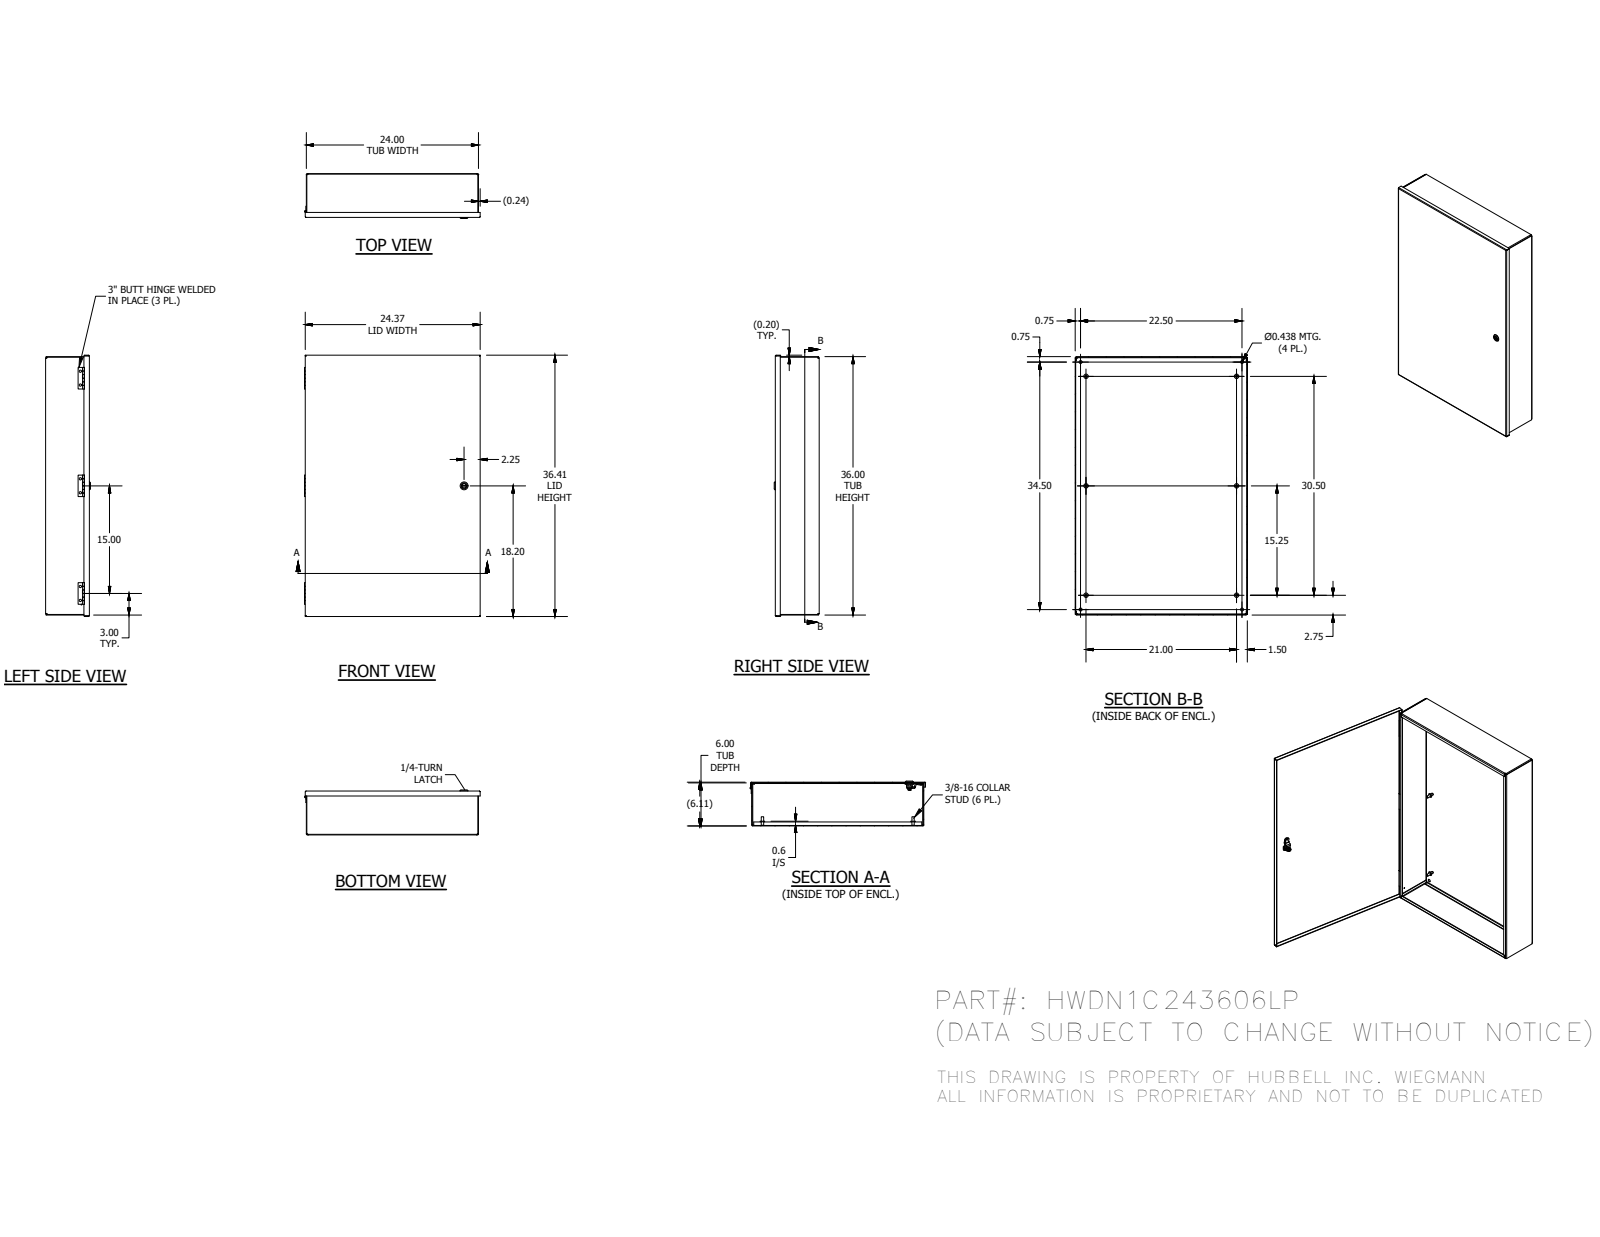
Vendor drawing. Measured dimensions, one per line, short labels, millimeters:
name: N1C243606LPBLR; N1C2406LPTB; N1C2436LPLID; 1000-101-GPF_GPD (+8 more)
written by: Autodesk Inventor 2016 (AUTOMOTIVE_DESIGN)
unit: mm
bodies: 26 solids, 780 faces (476 planar, 233 cylindrical, 71 other)
size: 924.72 × 622.01 × 178.12
volume: 3 314 000 mm³; area: 3 544 000 mm²
holes: 6× ⌀7.95, 4× ⌀11.11, 1× ⌀3.05, 1× ⌀3.3, 1× ⌀5, 1× ⌀8, 1× ⌀10, 1× ⌀10.2, 1× ⌀16.1, 1× ⌀20.38
bosses: 6× ⌀15.88, 6× ⌀8.38, 1× ⌀28, 1× ⌀27, 1× ⌀23, 1× ⌀19.8, 1× ⌀15.8, 1× ⌀15.2
rounds: 30× R0.3, 12× R1.59, 12× R3.47, 10× R0.5, 4× R0.79, 4× R2.67, 4× R4, 3× R0.4
face distances: 1.88, 172.24, 170.36, 174.12, 607.72, 912.52, 605.84, 609.6, 910.64, 914.4
hole spacings: 381, 49.28, 331.72, 430.28, 439.32, 571.5, 694.98, 762
